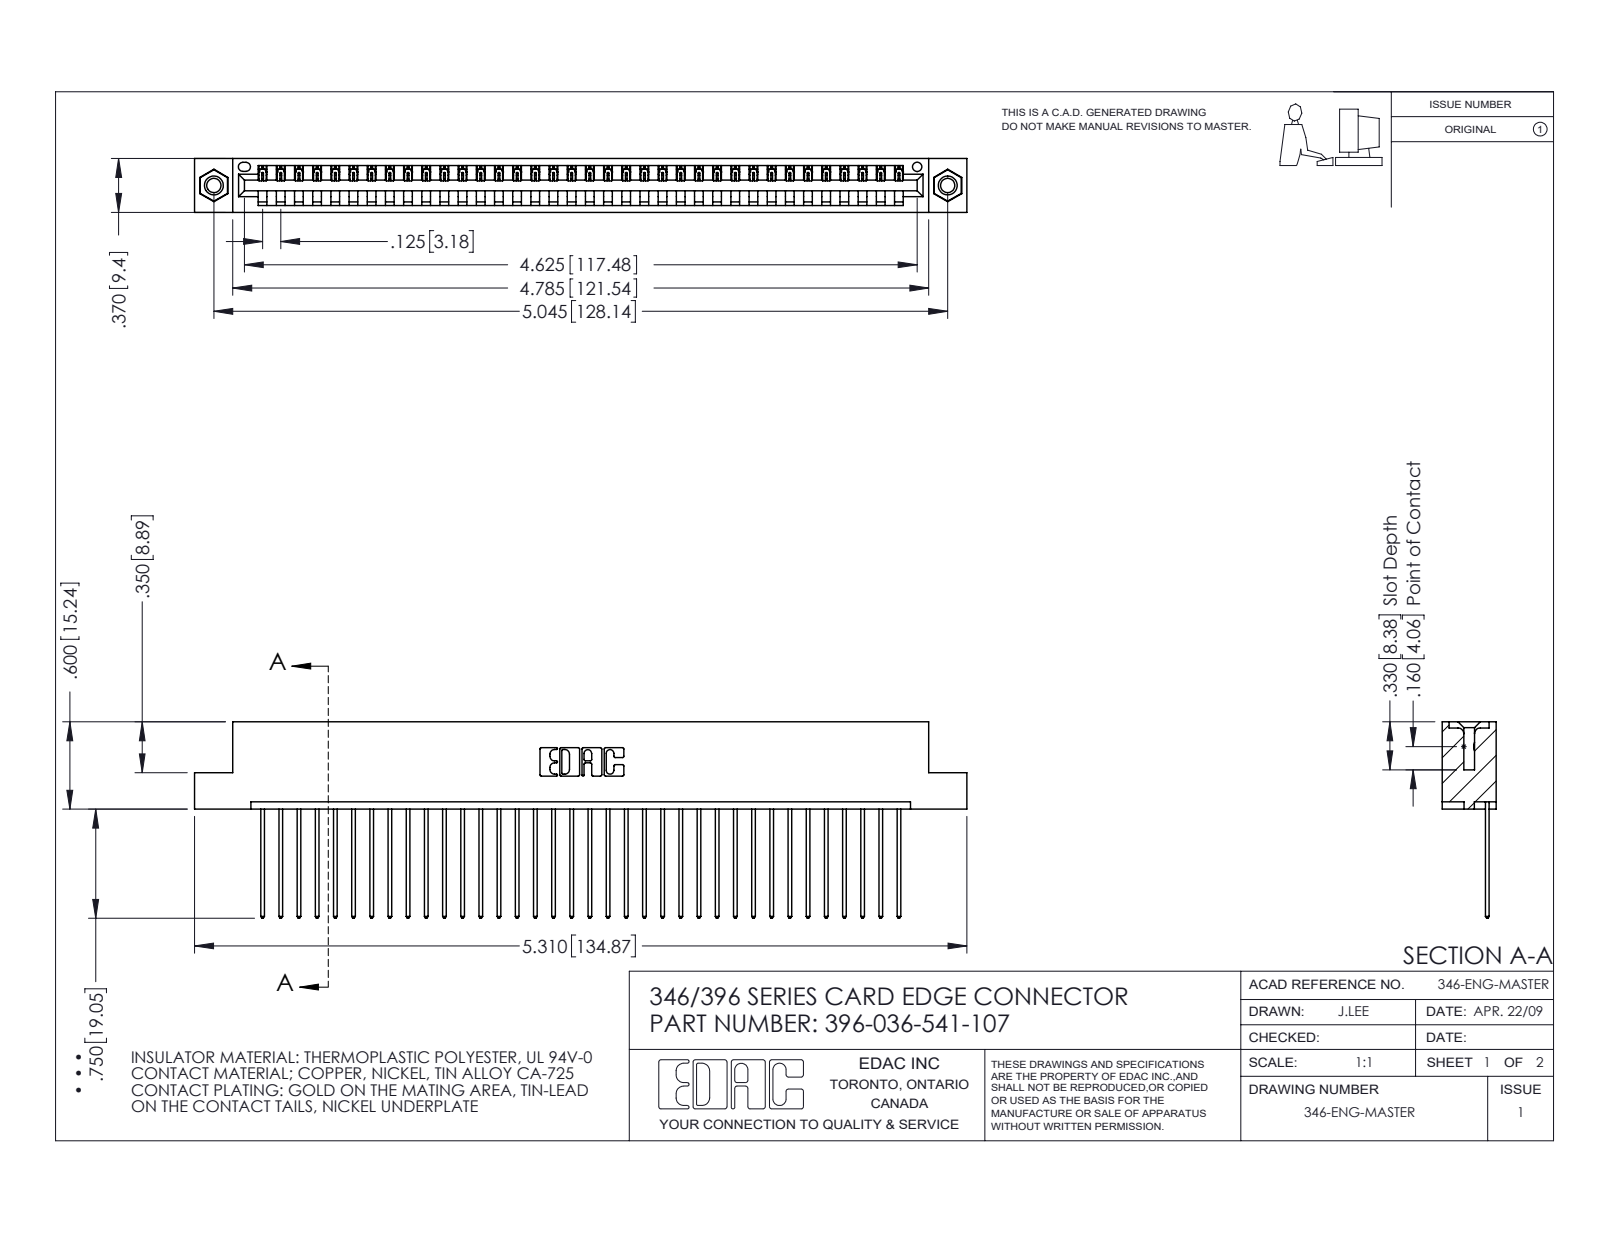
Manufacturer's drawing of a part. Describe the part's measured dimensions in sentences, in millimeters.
The part is named "396-036-541-107; 346 Part_Flush Mounting Lugs - 0.156 Dia-TI; 345-292-001_345-293-141; 345-250-001_345-250-005-103". Its 3-D file was written by "SolidWorks 2016 (CONFIG_CONTROL_DESIGN)". It is 39 solids with 2270 faces: 1548 planar, 706 cylindrical and 16 other. Overall it measures 134.9 by 34.3 by 9.4 millimeters. Its volume is 13 000 cubic millimeters and its surface area 16 900 square millimeters. Round holes: 2 of diameter 2.5, 2 of diameter 3.2, 2 of diameter 4, 1 of diameter 1.6. Round bosses or shafts: 2 of diameter 3.9. Partial cylindrical surfaces (rounded edges, fillets, slot ends): 72 of radius 0.2, 72 of radius 0.3, 22 of radius 0.3, 6 of radius 0.2, 6 of radius 0.8, 3 of radius 0.7, 2 of radius 0.8, 2 of radius 1. The main face-to-face distances are 1.2, 8.2, 9.4, 6.4, 1.8, 7.6, 0.6, 3.8, 5.6, 2.5. The hole center spacings are 6.2, 122.8, 128.1.
